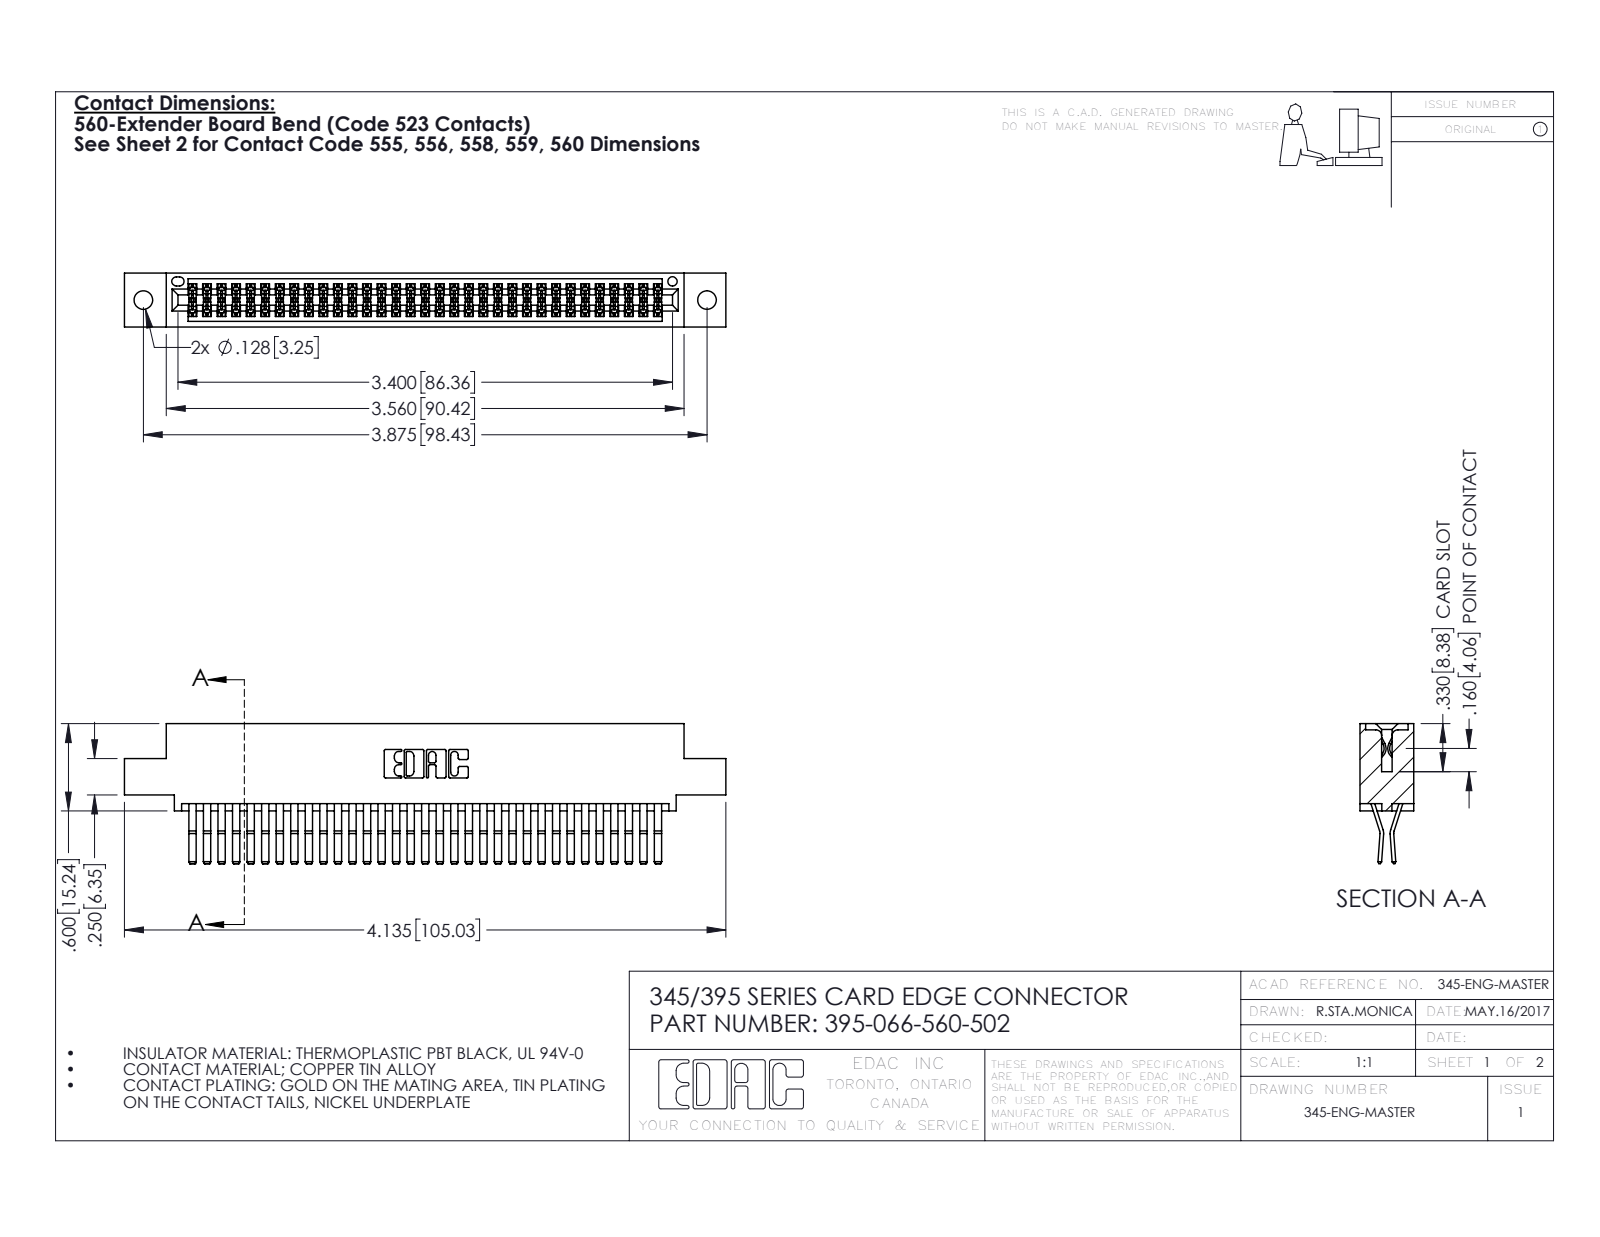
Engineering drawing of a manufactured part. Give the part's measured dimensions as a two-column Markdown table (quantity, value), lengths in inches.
| quantity | value |
| --- | --- |
| part name | 395-066-560-502; 345 Part_0.110 Offset - 0.128 Dia; 345-292-001_560 Tail |
| STEP written by | SolidWorks 2016 (CONFIG_CONTROL_DESIGN) |
| units | inches |
| bodies | 67 solids, 3562 faces (2262 planar, 1300 cylindrical, 0 other) |
| overall size | 4.135 × 0.962 × 0.37 |
| volume | 0.637 in³ |
| surface area | 25.1 in² |
| round holes (diameter × count) | 0.128 × 2, 0.064 × 1 |
| partial cylindrical surfaces (radius × count) | 0.006 × 100, 0.01 × 22, 0.007 × 6, 0.031 × 6, 0.026 × 3, 0.01 × 2, 0.014 × 2, 0.019 × 2 |
| main face-to-face distances | 0.025, 0.298, 0.072, 0.2, 0.37, 0.098, 0.272, 0.225, 0.175, 0.149 |
| hole center spacings | 0.27, 3.64, 3.875 |
